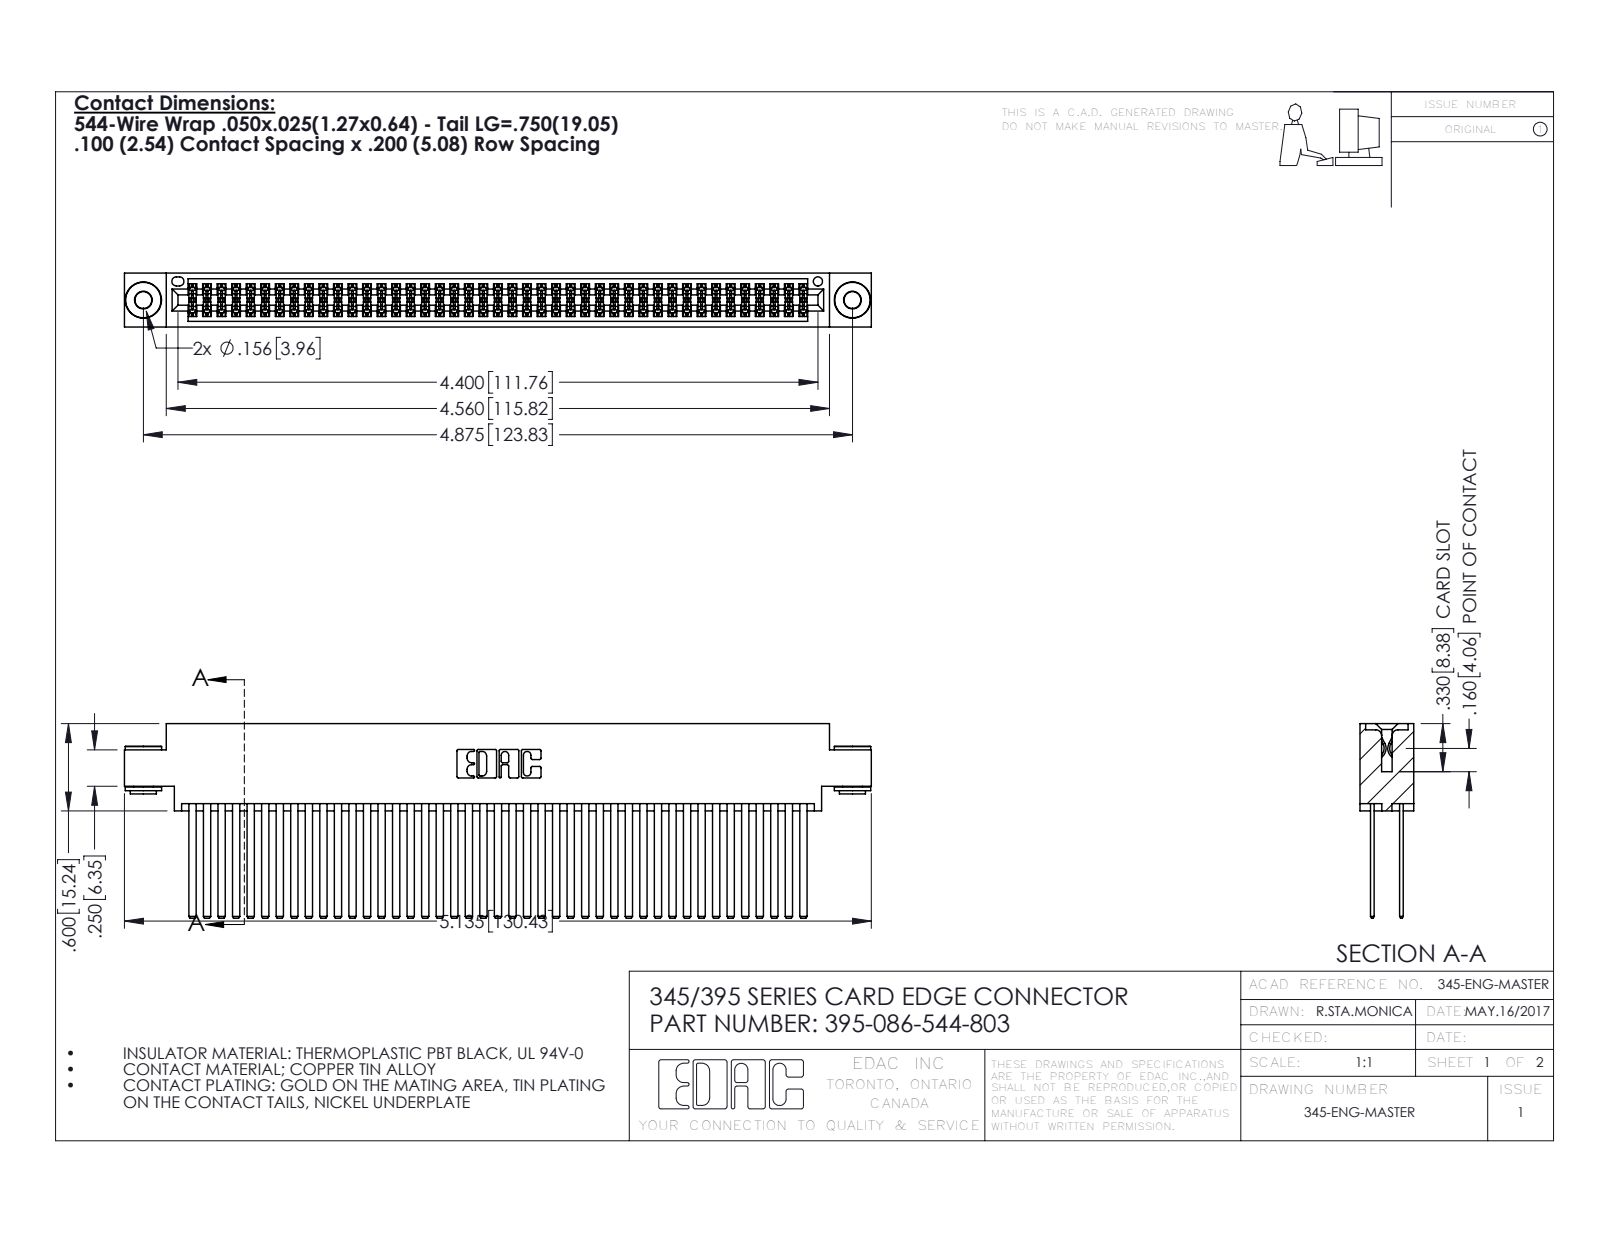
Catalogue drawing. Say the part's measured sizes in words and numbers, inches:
The part is named "345-292-001_345-293-144; 345 Part_0.170 Offset - 0.156 Dia-TH; 395-086-544-803; 345-250-002_345-250-002-102". Its 3-D file was written by "SolidWorks 2016 (CONFIG_CONTROL_DESIGN)". It is 89 solids with 3952 faces: 2588 planar, 1356 cylindrical and 8 other. Overall it measures 5.135 by 1.337 by 0.37 inches. Its volume is 0.842 cubic inches and its surface area 37.64 square inches. Round holes: 2 of diameter 0.116, 2 of diameter 0.156, 1 of diameter 0.064. Round bosses or shafts: 2 of diameter 0.25, 2 of diameter 0.18, 2 of diameter 0.136. Partial cylindrical surfaces (rounded edges, fillets, slot ends): 129 of radius 0.006, 22 of radius 0.01, 6 of radius 0.007, 6 of radius 0.031, 3 of radius 0.026, 2 of radius 0.014, 2 of radius 0.019, 2 of radius 0.022. The main face-to-face distances are 0.2, 0.025, 0.072, 0.098, 0.272, 0.298, 0.225, 0.175, 0.37, 0.15. The hole center spacings are 0.27, 4.639, 4.875.
